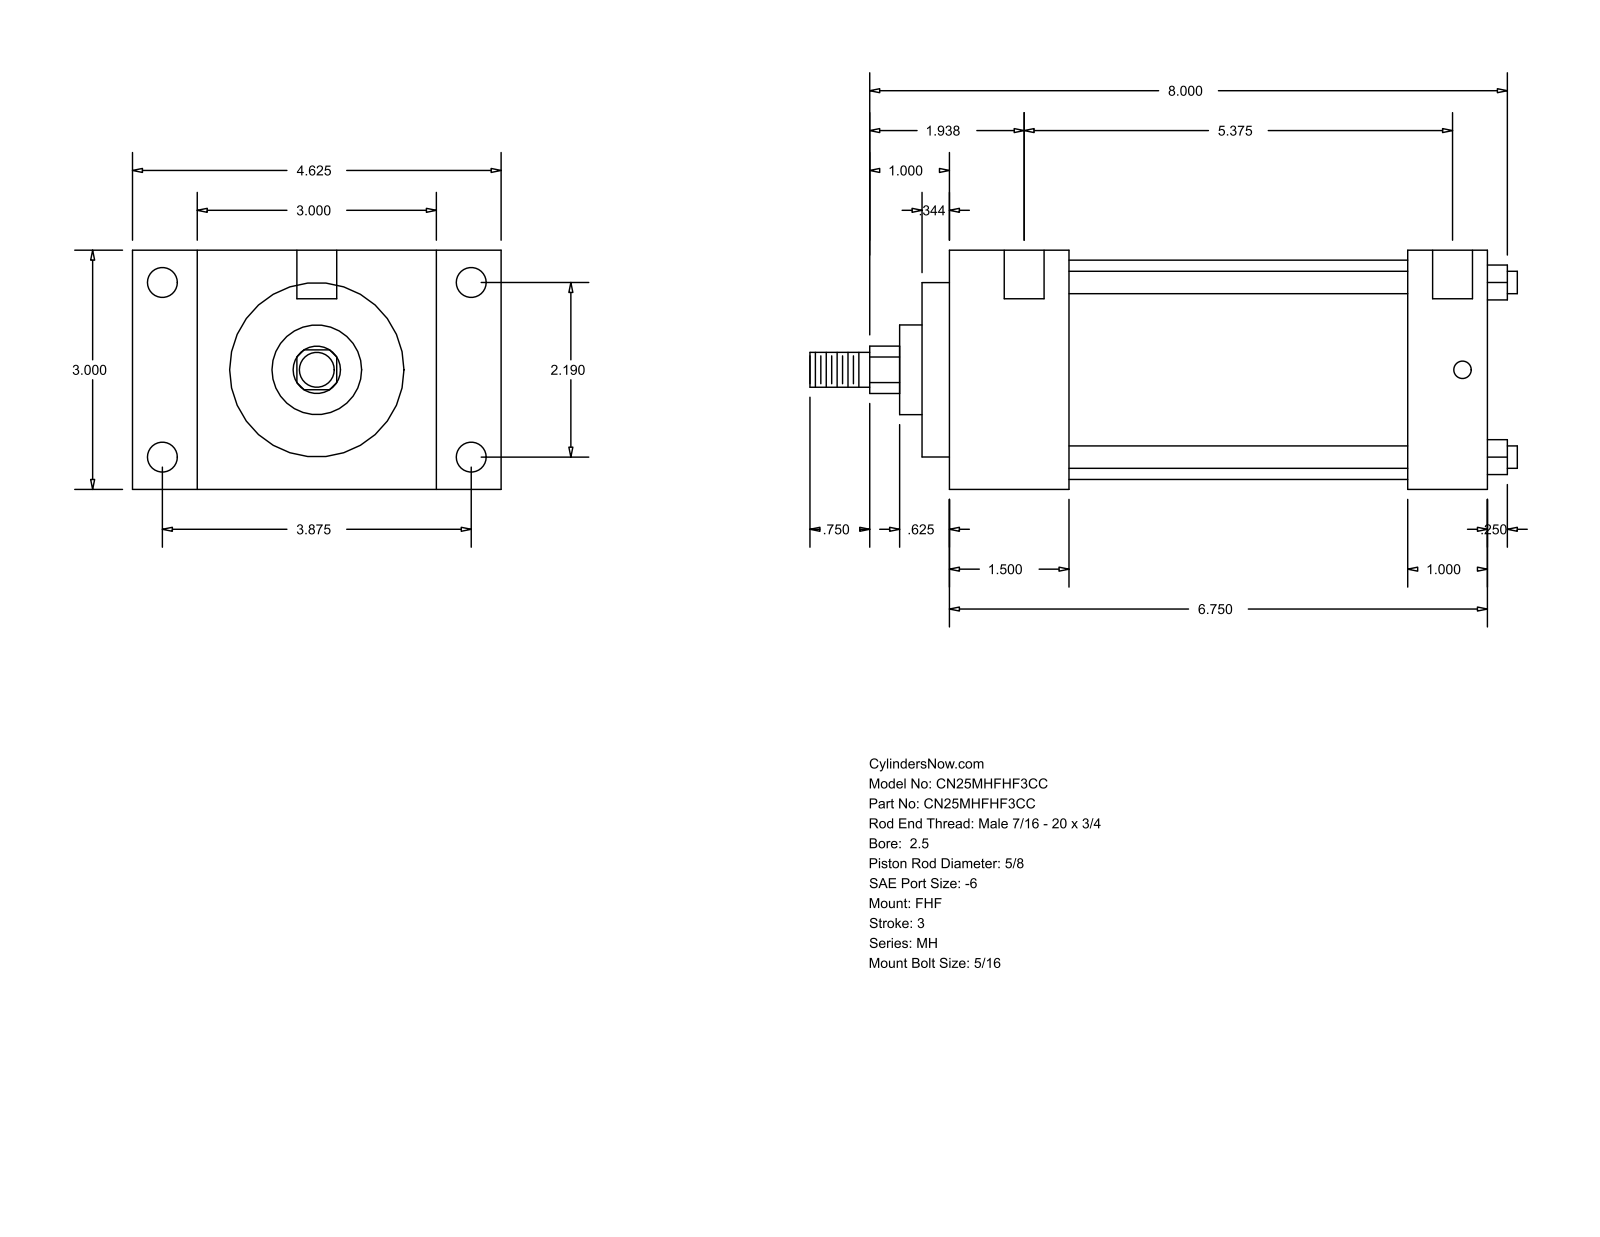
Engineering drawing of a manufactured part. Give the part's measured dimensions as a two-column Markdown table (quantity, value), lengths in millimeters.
| quantity | value |
| --- | --- |
| part name | MH_FHF__0250_0.625 |
| STEP written by | GSSL Pune (CONFIG_CONTROL_DESIGN) |
| units | millimeters |
| bodies | 0 solids, 90 faces (61 planar, 29 cylindrical, 0 other) |
| overall size | 225.43 × 117.47 × 76.2 |
| round holes (diameter × count) | 5.56 × 4, 9.53 × 4, 12.7 × 2 |
| round bosses / shafts (diameter × count) | 7.14 × 4, 69.85 × 1, 55.55 × 1, 28.57 × 1, 15.88 × 1, 11.11 × 1 |
| partial cylindrical surfaces (radius × count) | 7.54 × 1 |
| main face-to-face distances | 76.2, 171.45, 38.1, 133.35, 20.64, 96.84, 117.48, 25.4, 146.05, 107.95 |
| hole center spacings | 55.62, 98.42, 113.05, 144.46, 3.17, 4.76, 136.53, 139.7 |
